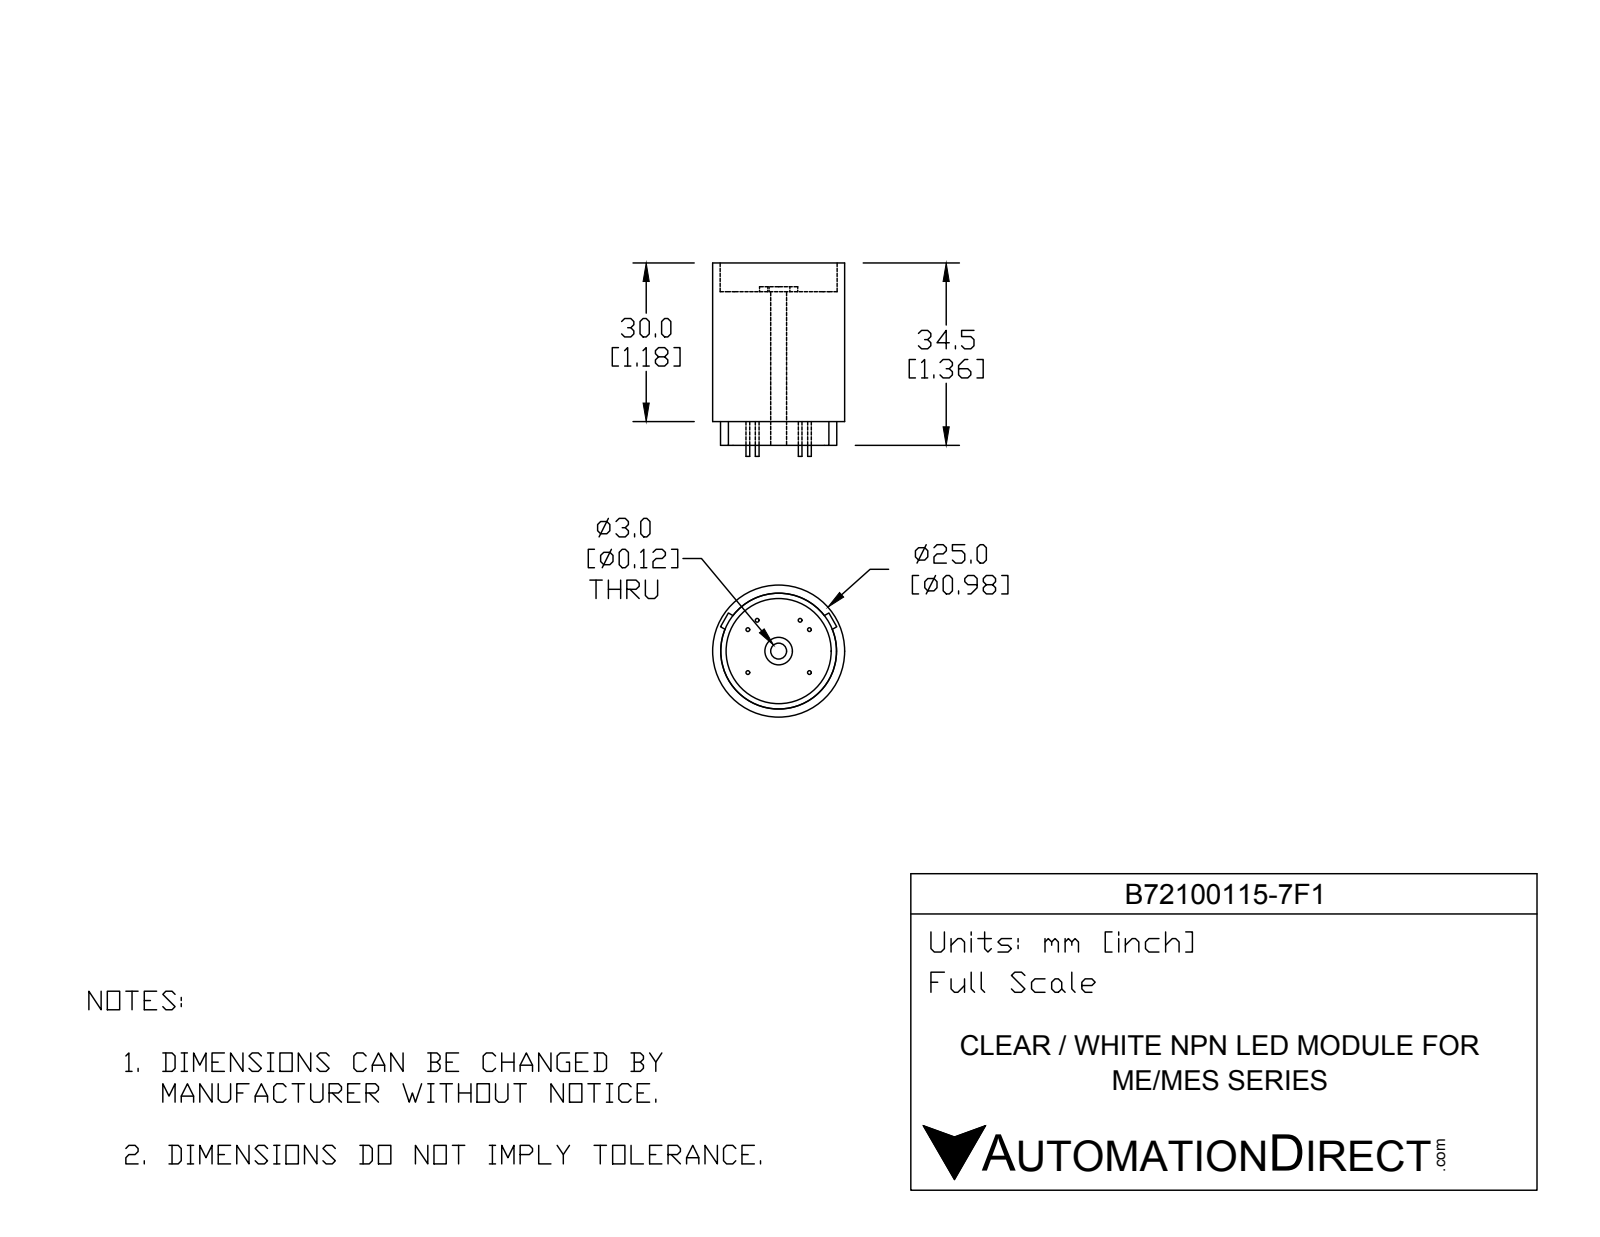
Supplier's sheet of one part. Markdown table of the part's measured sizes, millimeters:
| quantity | value |
| --- | --- |
| part name | B72100115-7F1 |
| STEP written by | SolidWorks 2016 (AUTOMOTIVE_DESIGN) |
| units | millimeters |
| bodies | 9 solids, 69 faces (36 planar, 33 cylindrical, 0 other) |
| overall size | 36.6 × 25 × 25 |
| volume | 12 963 mm³ |
| surface area | 4 884 mm² |
| round holes (diameter × count) | 3 × 1, 4.22 × 1, 19.9 × 1, 21.5 × 1 |
| round bosses / shafts (diameter × count) | 0.7 × 6, 25 × 1, 21.9 × 1, 7.22 × 1, 5.2 × 1 |
| main face-to-face distances | 24.56, 30, 5.44, 4.5, 29.06, 34.5, 25.5, 0.94, 3.05, 3.1 |
